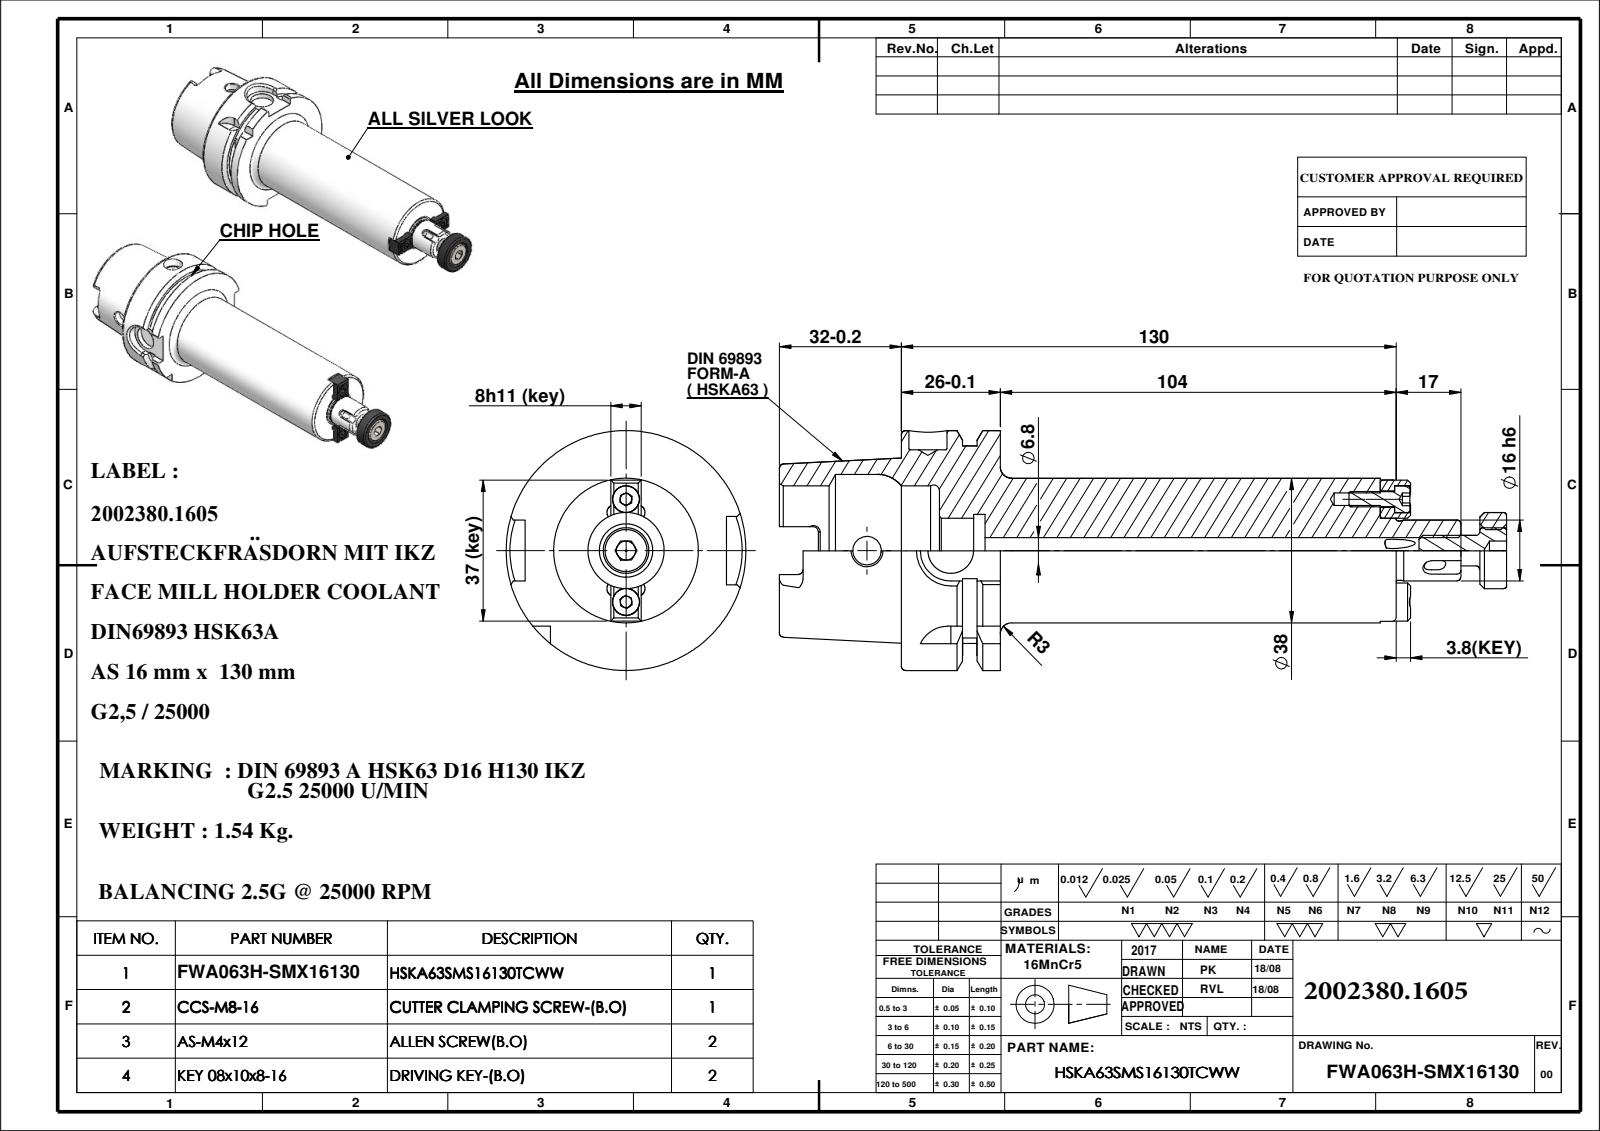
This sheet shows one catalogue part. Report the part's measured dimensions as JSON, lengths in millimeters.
{"part_name": "HSKA63SMS16130TCWW; 9163A-AS516130; AS-M4X12_DIN 912 M4 x 10 --- 10N; CCS-M8-16-SHORT LENGHT (+3 more)", "step_written_by": "SolidWorks 2009 (CONFIG_CONTROL_DESIGN)", "units": "millimeters", "bodies": {"solids": 7, "faces": 369, "planar": 147, "cylindrical": 97, "other": 125}, "overall_size": [191, 63, 63], "volume_mm3": 200847, "surface_area_mm2": 42526, "round_holes": [[3, 4], [3.3, 2], [4.4, 2], [7.1, 2], [6.8, 1], [7.5, 1], [10, 1], [11, 1], [12, 1], [17, 1], [19, 1], [34, 1]], "round_bosses_or_shafts": [[7, 2], [4, 2], [63, 1], [55, 1], [38, 1], [20, 1], [16, 1], [15.6, 1]], "partial_cylinders_radius": [[2, 8], [1.3, 6], [2.88, 4], [8, 2], [9, 1]], "face_to_face_distances": [26, 130, 10, 104, 16, 120, 32, 42, 58, 162], "hole_center_spacings": [13.5, 22, 27]}
